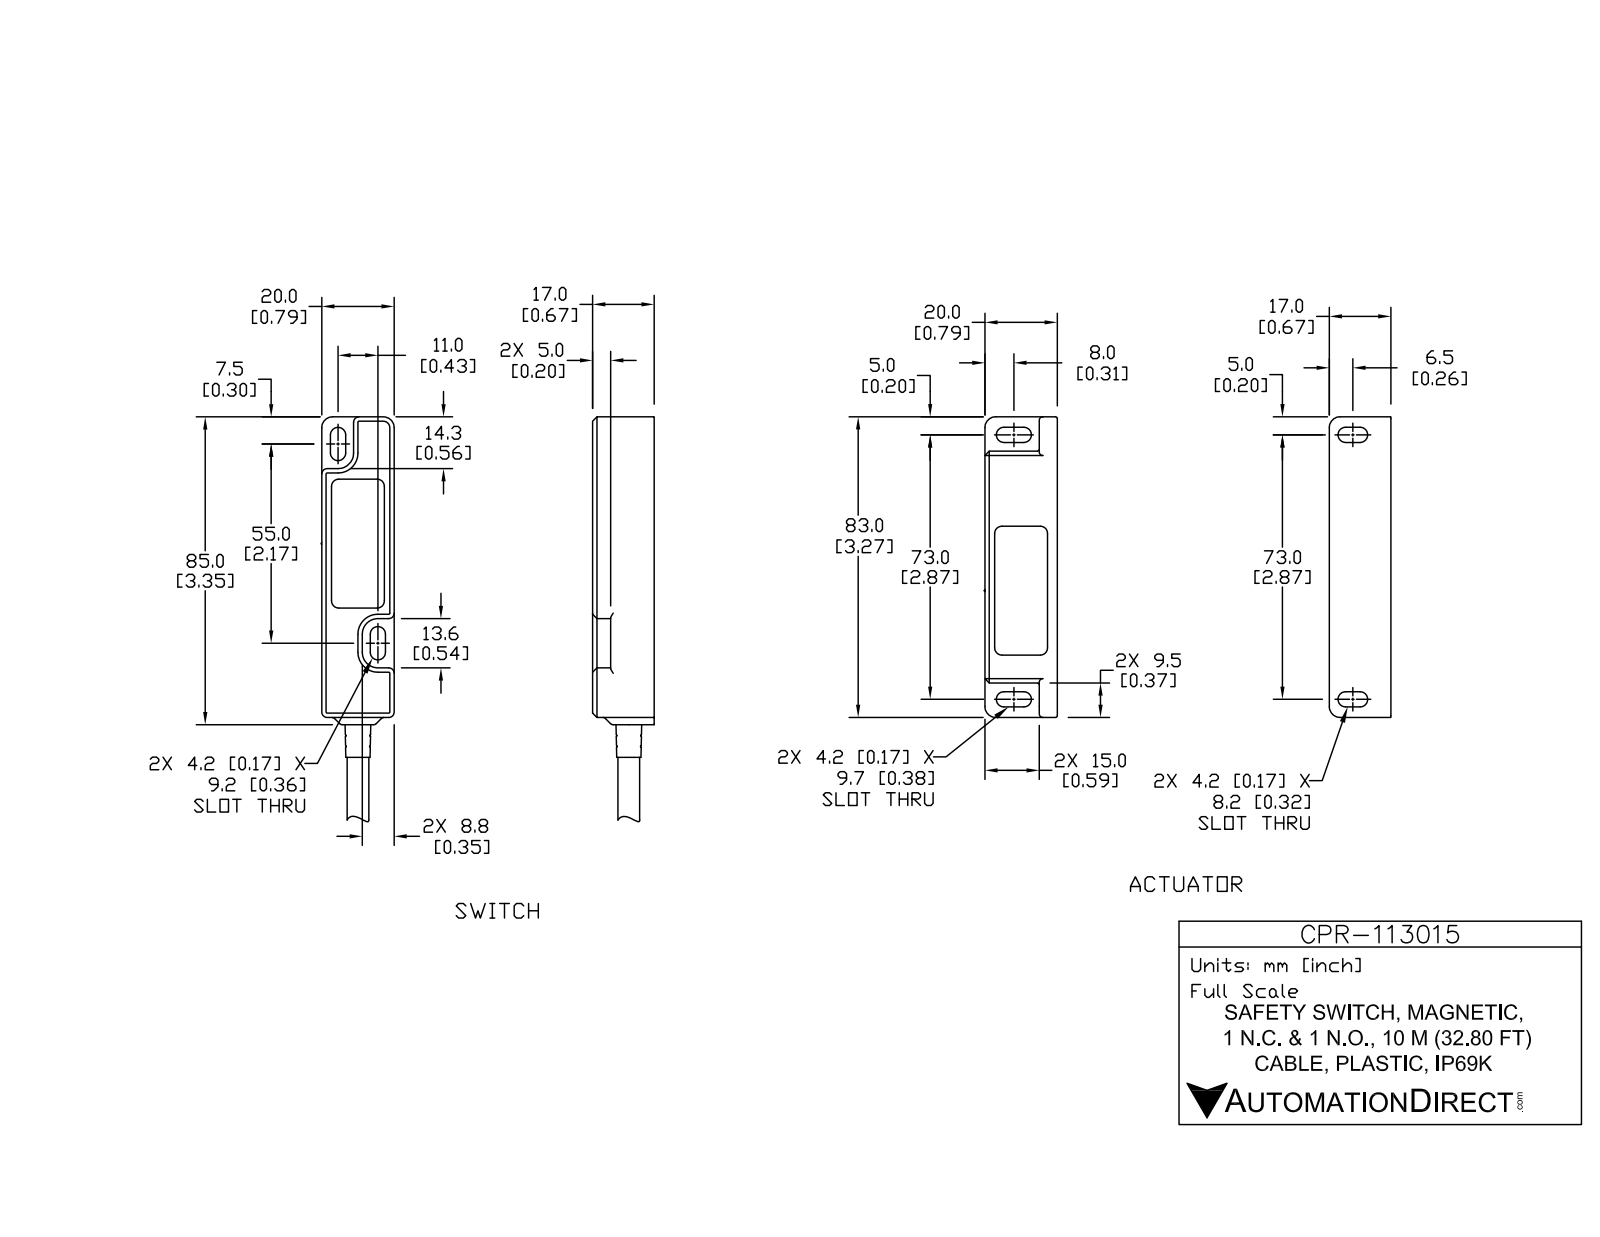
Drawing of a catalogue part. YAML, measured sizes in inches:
part_name: "CPR-113015_2; CPR-113015_1; CPR-113015"
step_written_by: "SolidWorks 2017 (AUTOMOTIVE_DESIGN)"
units: inches
bodies: {solids: 4, faces: 194, planar: 77, cylindrical: 69, other: 48}
overall_size: [7.169, 1.614, 0.669]
volume: 3.243
surface_area: 25.07
round_bosses_or_shafts:
  - {diameter: 0.236, count: 1}
partial_cylinders:
  - {radius: 0.083, count: 12}
  - {radius: 0.039, count: 10}
  - {radius: 0.02, count: 8}
  - {radius: 0.079, count: 8}
  - {radius: 0.059, count: 6}
  - {radius: 0.118, count: 6}
  - {radius: 0.028, count: 3}
  - {radius: 0.169, count: 3}
face_to_face_distances: [0.827, 0.787, 0.669, 1.614, 0.657, 0.039, 0.197, 0.472, 0.374, 2.894]
